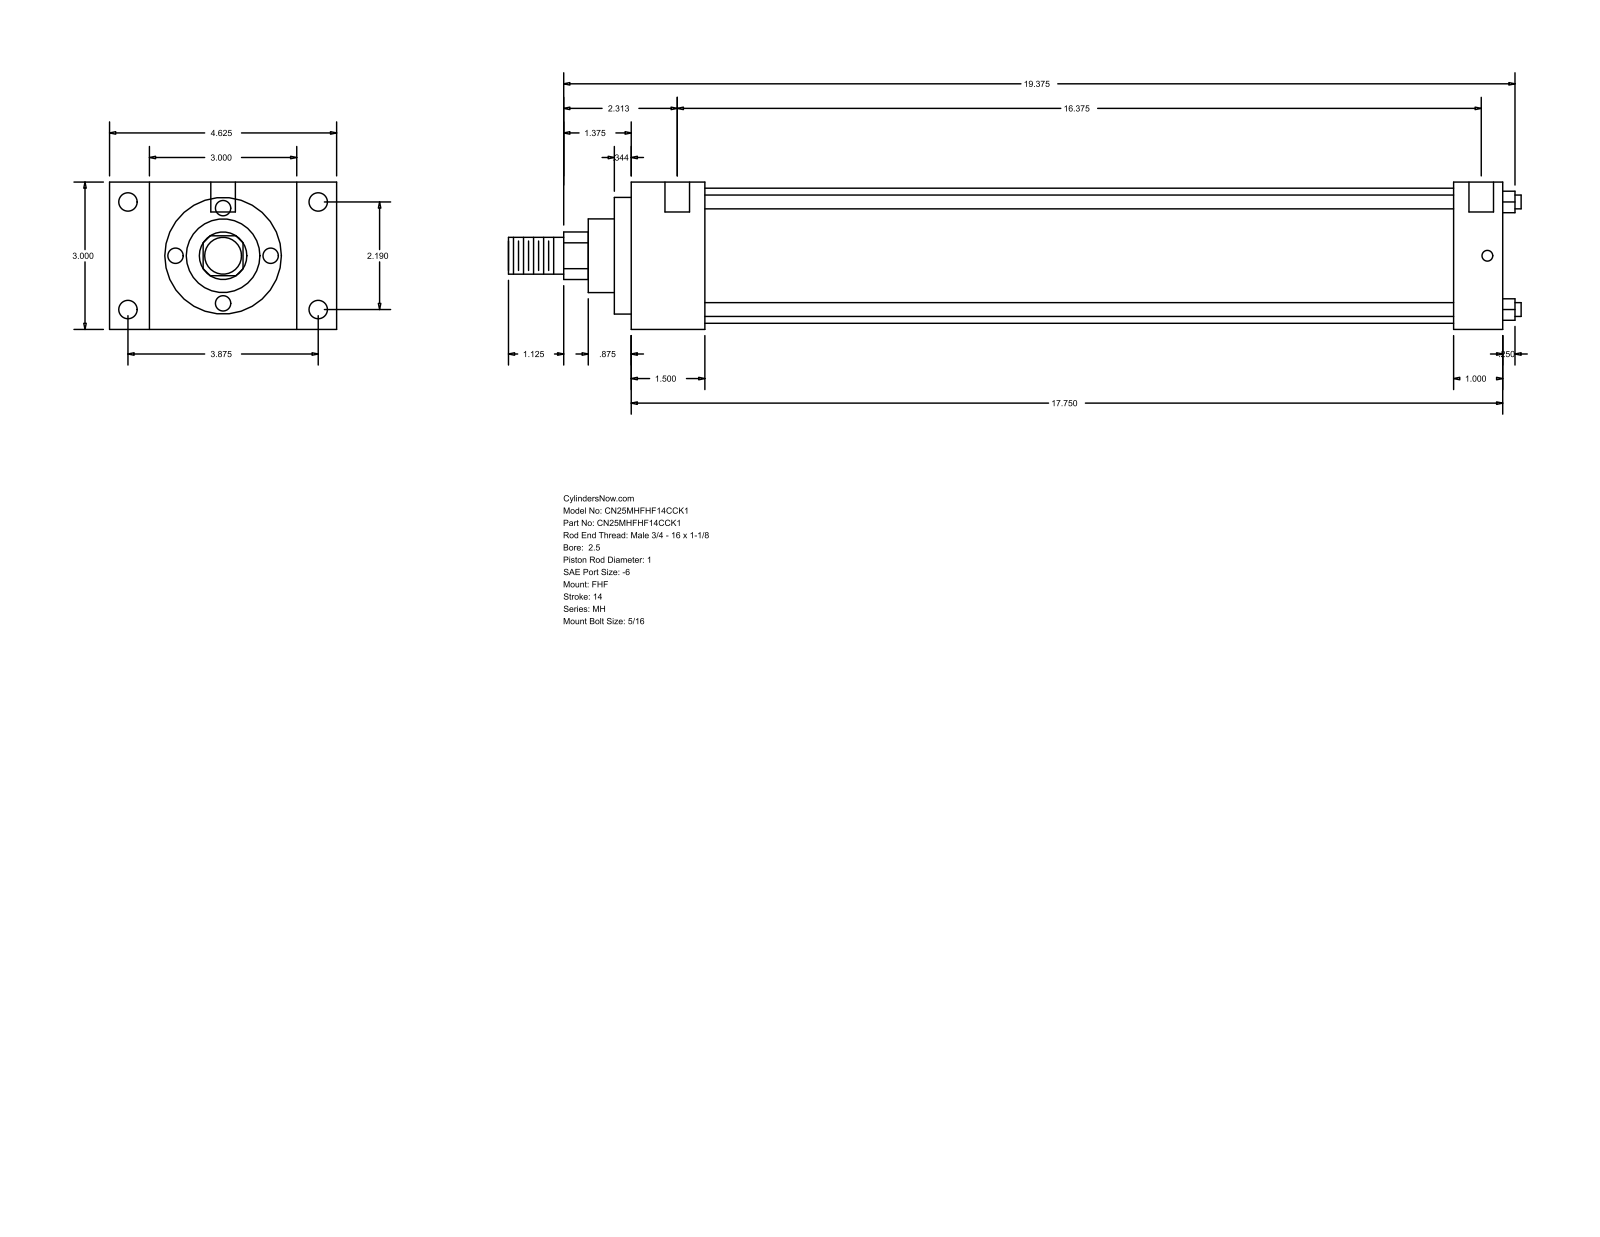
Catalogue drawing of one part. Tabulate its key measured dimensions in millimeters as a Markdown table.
| quantity | value |
| --- | --- |
| part name | MH_FHF__0250_1 |
| STEP written by | GSSL Pune (CONFIG_CONTROL_DESIGN) |
| units | millimeters |
| bodies | 0 solids, 90 faces (61 planar, 29 cylindrical, 0 other) |
| overall size | 523.88 × 117.47 × 76.2 |
| round holes (diameter × count) | 5.56 × 4, 9.53 × 4, 12.7 × 2 |
| round bosses / shafts (diameter × count) | 7.14 × 4, 69.85 × 1, 60.33 × 1, 38.1 × 1, 25.4 × 1, 19.05 × 1 |
| partial cylindrical surfaces (radius × count) | 12.29 × 1 |
| main face-to-face distances | 76.2, 450.85, 38.11, 412.74, 20.64, 96.84, 117.48, 25.39, 425.46, 387.35 |
| hole center spacings | 55.62, 98.42, 113.05, 423.86, 3.18, 4.76, 415.92, 419.1 |
